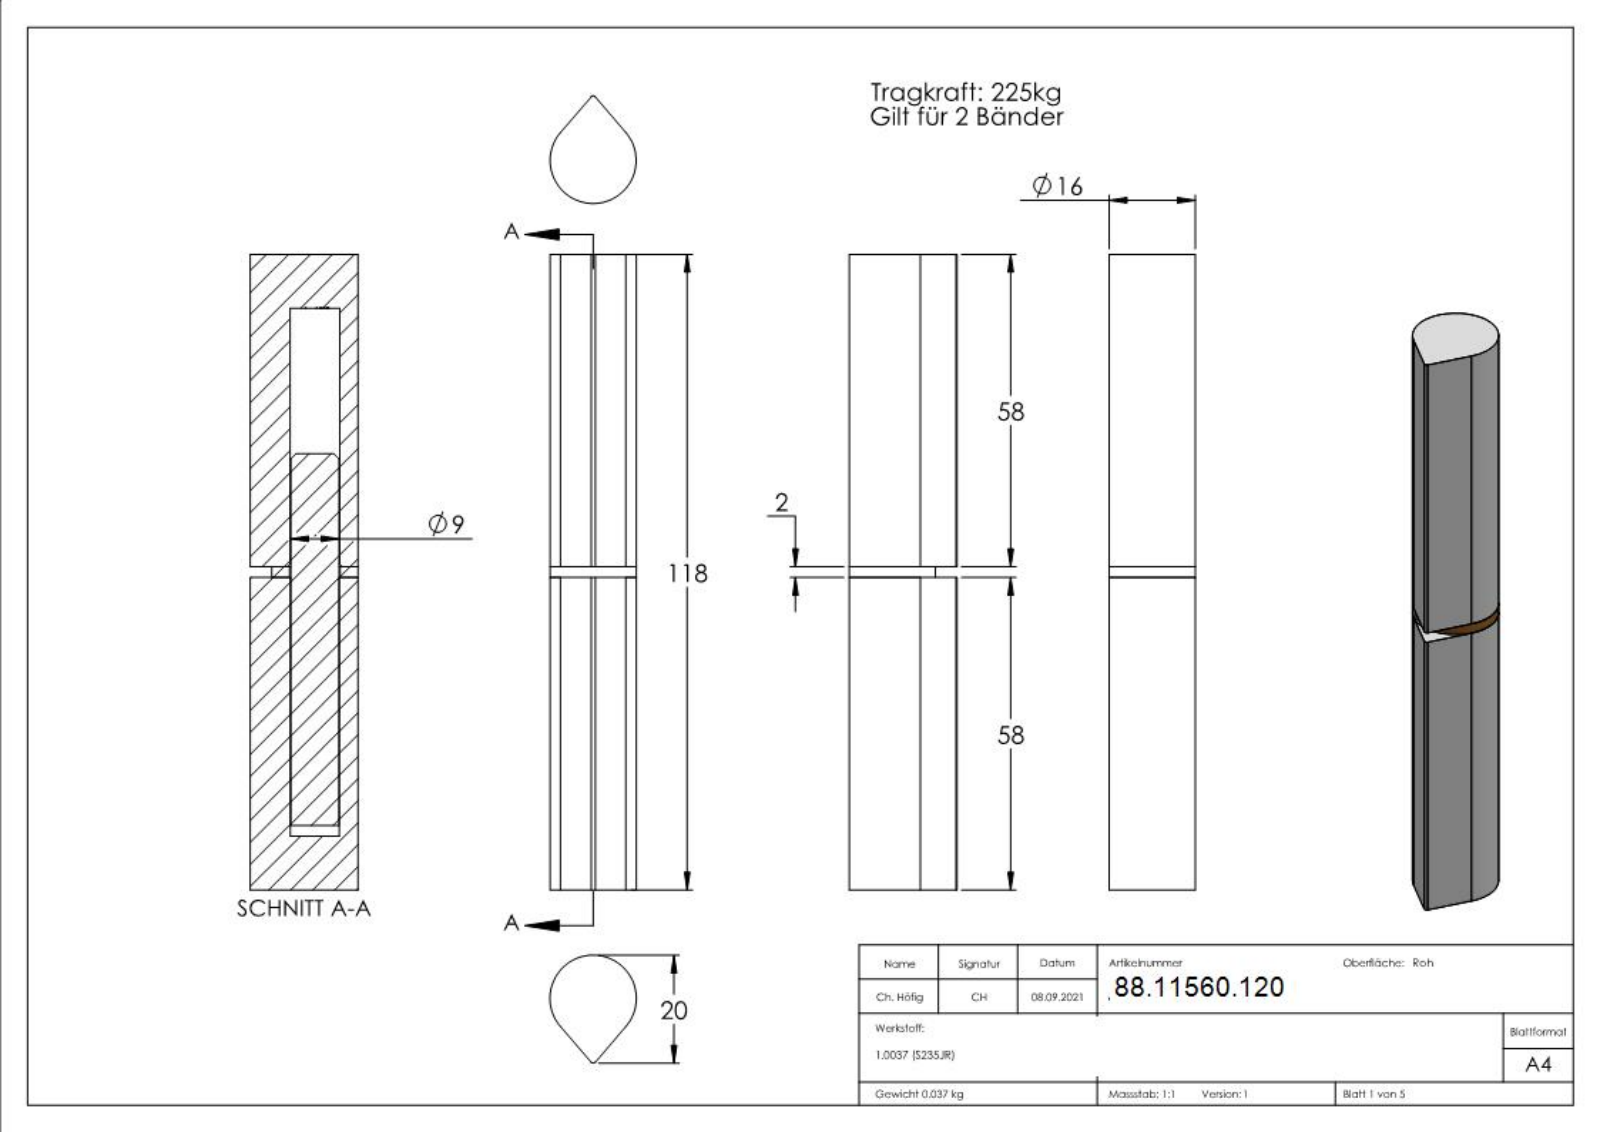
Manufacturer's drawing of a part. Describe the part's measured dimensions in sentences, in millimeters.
The part is named "560-xx Teil1; 560-120; 560-xx Teil3; 560-xx Teil2 (+3 more)". Its 3-D file was written by "SolidWorks 2018 (CONFIG_CONTROL_DESIGN)". It is 4 solids with 257 faces: 137 planar, 9 cylindrical and 111 other. Overall it measures 118 by 20 by 16 millimeters. Its volume is 23 845 cubic millimeters and its surface area 12 484 square millimeters. Round holes: 1 of diameter 9.1, 1 of diameter 9.25, 1 of diameter 9.4. Round bosses or shafts: 1 of diameter 16, 1 of diameter 9. Partial cylindrical surfaces (rounded edges, fillets, slot ends): 1 of radius 0.5. The main face-to-face distances are 58, 60, 2, 118, 48, 10, 108, 50, 98, 12.
